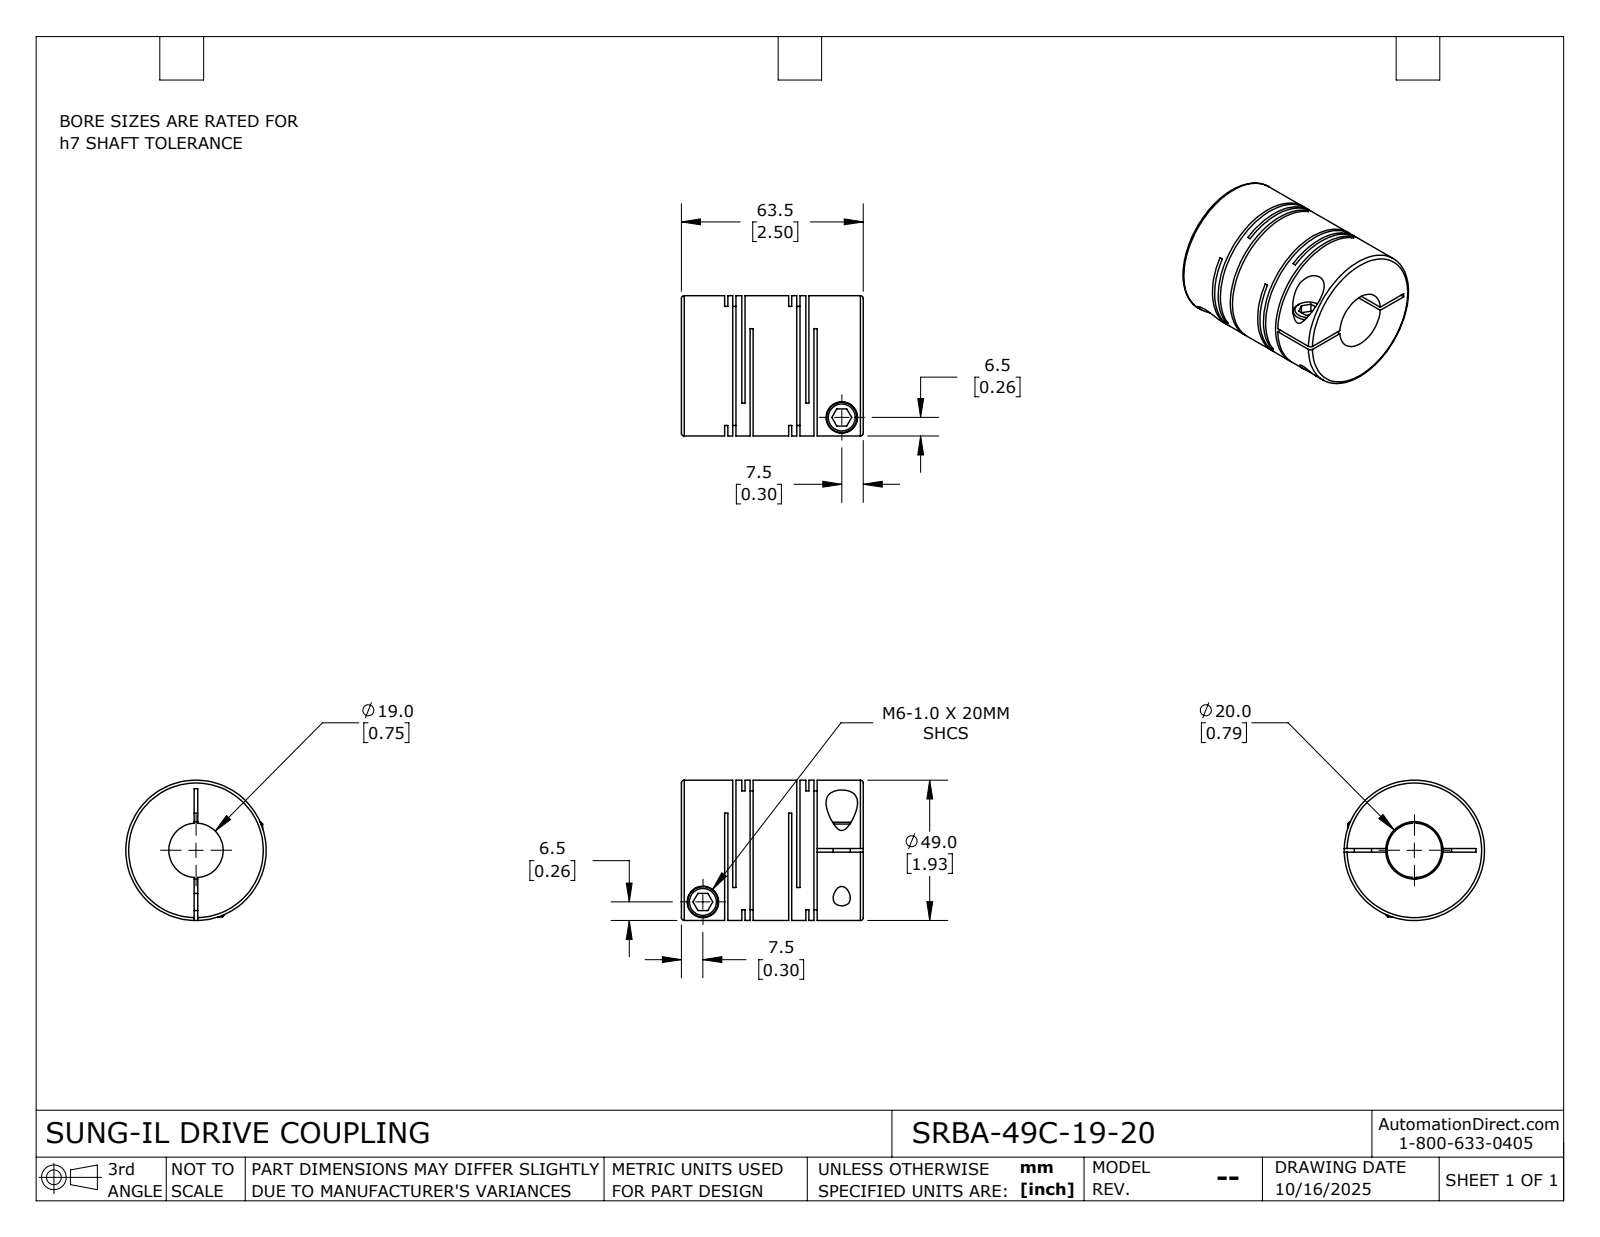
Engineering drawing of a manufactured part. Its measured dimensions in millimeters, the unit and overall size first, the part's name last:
Units: millimetres
Overall size (bounding box): 63.5 × 49 × 49
Round holes (diameter × count): ⌀6 ×2, ⌀11 ×2, ⌀19 ×1, ⌀20 ×1
Round bosses / shafts (diameter × count): ⌀10.6 ×2, ⌀49 ×1
Main face-to-face distances: 6, 1.1, 22.35, 2.85, 21.25, 3.15, 1.75, 4.9, 19.5, 16.35
Volume: 86 652 mm³ · Surface area: 38 016 mm²
Bodies: 1 solid, 115 faces (60 planar, 42 cylindrical, 13 other)
Part name (STEP PRODUCT): SRBA-49C-19-20
STEP written by: SolidWorks 2024 (CONFIG_CONTROL_DESIGN)
